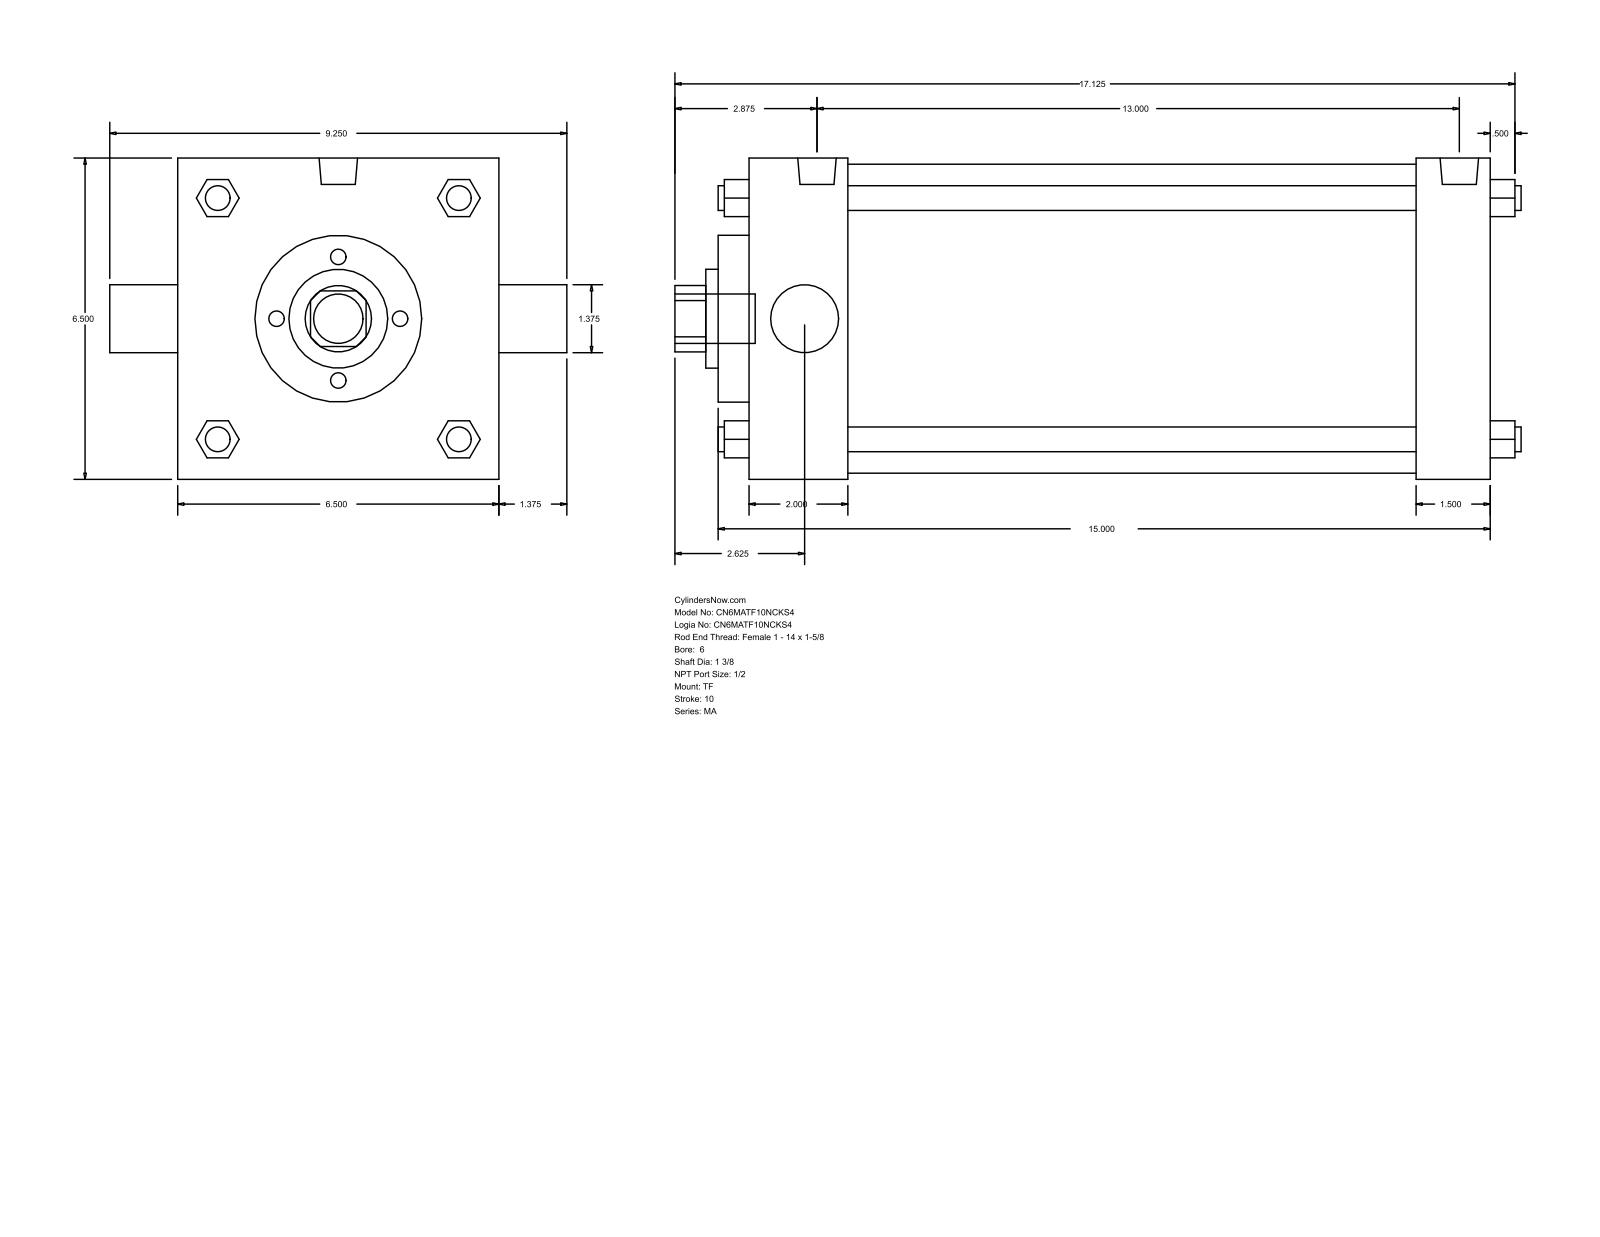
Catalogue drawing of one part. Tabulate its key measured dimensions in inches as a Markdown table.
| quantity | value |
| --- | --- |
| part name | MA_TF__0600_1.375 |
| STEP written by | GSSL Pune (CONFIG_CONTROL_DESIGN) |
| units | inches |
| bodies | 0 solids, 122 faces (93 planar, 29 cylindrical, 0 other) |
| overall size | 17.125 × 9.25 × 6.5 |
| round holes (diameter × count) | 1.375 × 2, 2 × 1, 3.375 × 1, 6.25 × 1 |
| round bosses / shafts (diameter × count) | 0.5 × 4, 0.687 × 3, 0.778 × 2, 1 × 1 |
| partial cylindrical surfaces (radius × count) | 0.672 × 1 |
| main face-to-face distances | 6.5, 15.125, 2, 13.625, 13.125, 11.625, 1.5, 0.625, 2.625, 14.25 |
